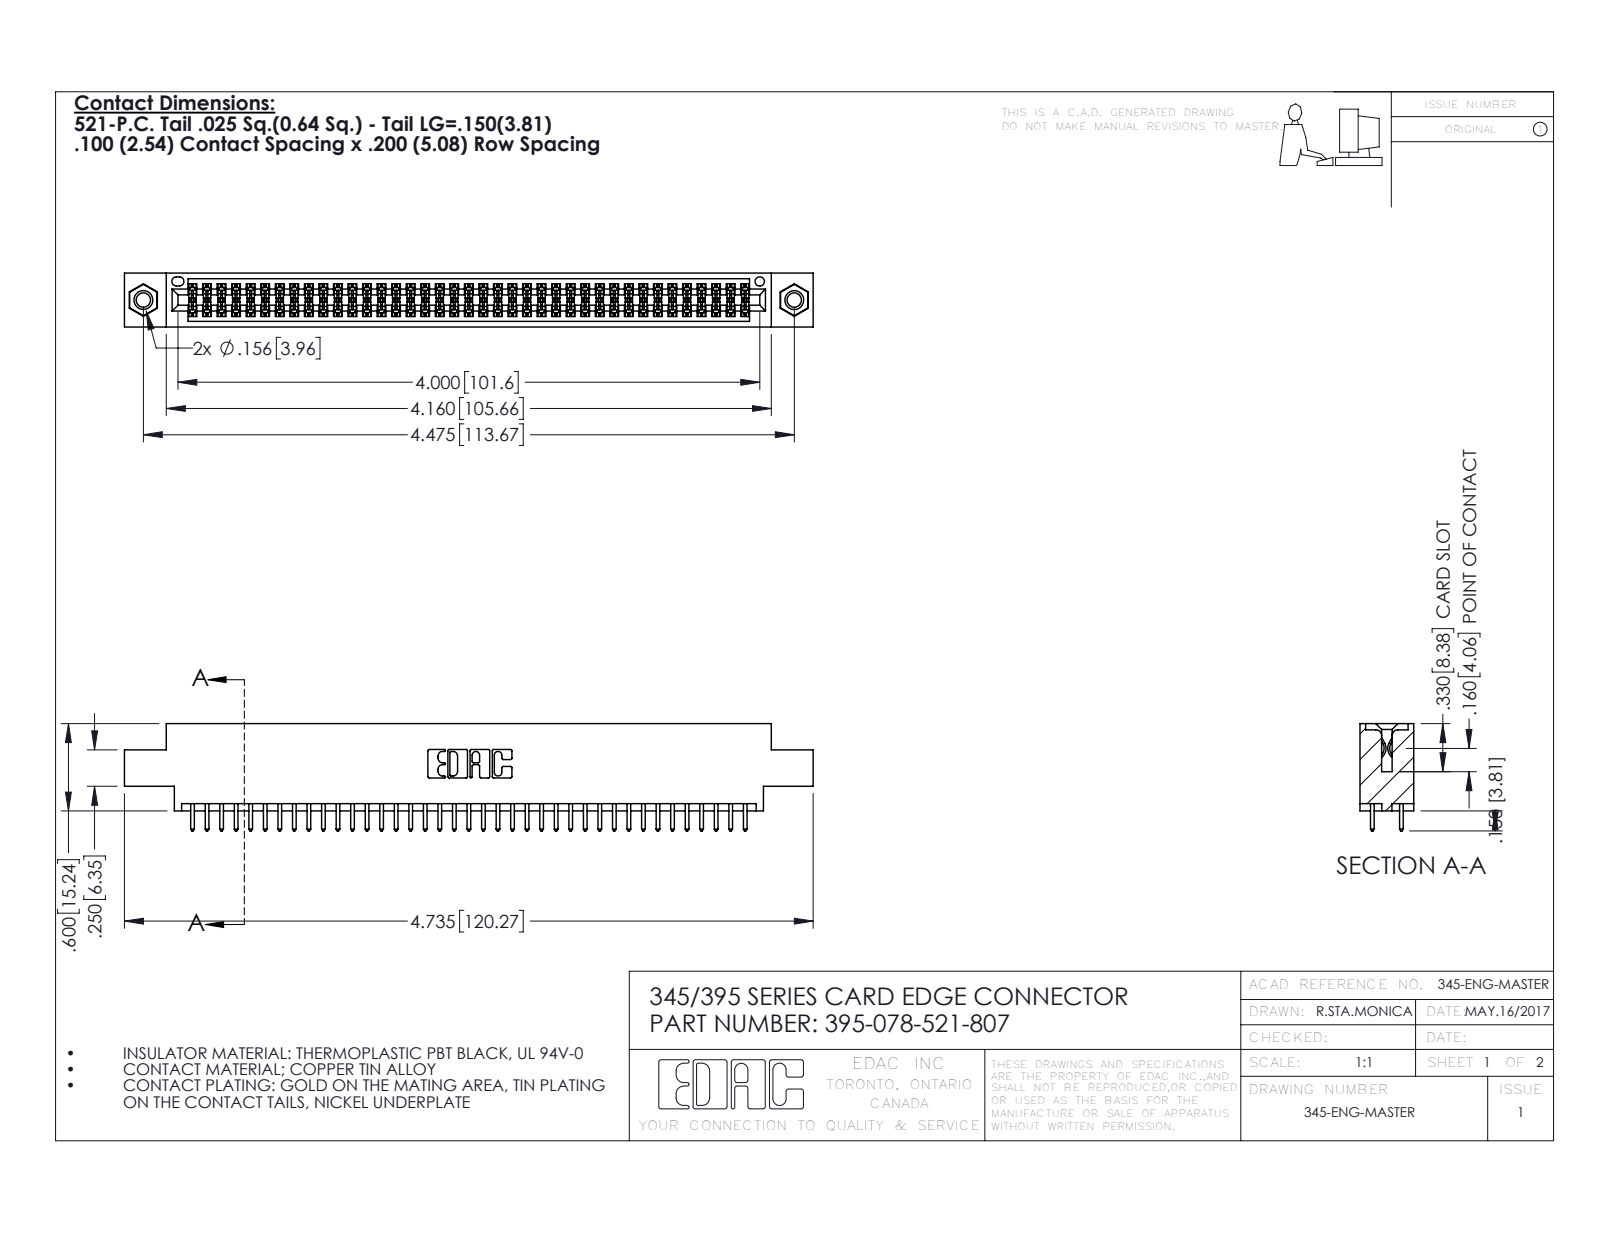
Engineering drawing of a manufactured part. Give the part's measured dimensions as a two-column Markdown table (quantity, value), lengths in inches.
| quantity | value |
| --- | --- |
| part name | 345-250-001_345-250-005-103; 345 Part_0.170 Offset - 0.156 Dia-TI; 395-078-521-807; 345-292-001_345-293-121 |
| STEP written by | SolidWorks 2016 (CONFIG_CONTROL_DESIGN) |
| units | inches |
| bodies | 81 solids, 4090 faces (2690 planar, 1384 cylindrical, 16 other) |
| overall size | 4.735 × 0.737 × 0.37 |
| volume | 0.702 in³ |
| surface area | 26.19 in² |
| round holes (diameter × count) | 0.098 × 2, 0.125 × 2, 0.156 × 2, 0.064 × 1 |
| round bosses / shafts (diameter × count) | 0.155 × 2 |
| partial cylindrical surfaces (radius × count) | 0.006 × 117, 0.01 × 78, 0.01 × 22, 0.007 × 6, 0.031 × 6, 0.026 × 3, 0.014 × 2, 0.019 × 2 |
| main face-to-face distances | 0.072, 0.298, 0.37, 0.2, 0.098, 0.272, 0.025, 0.225, 0.175, 0.149 |
| hole center spacings | 0.27, 4.239, 4.475 |
